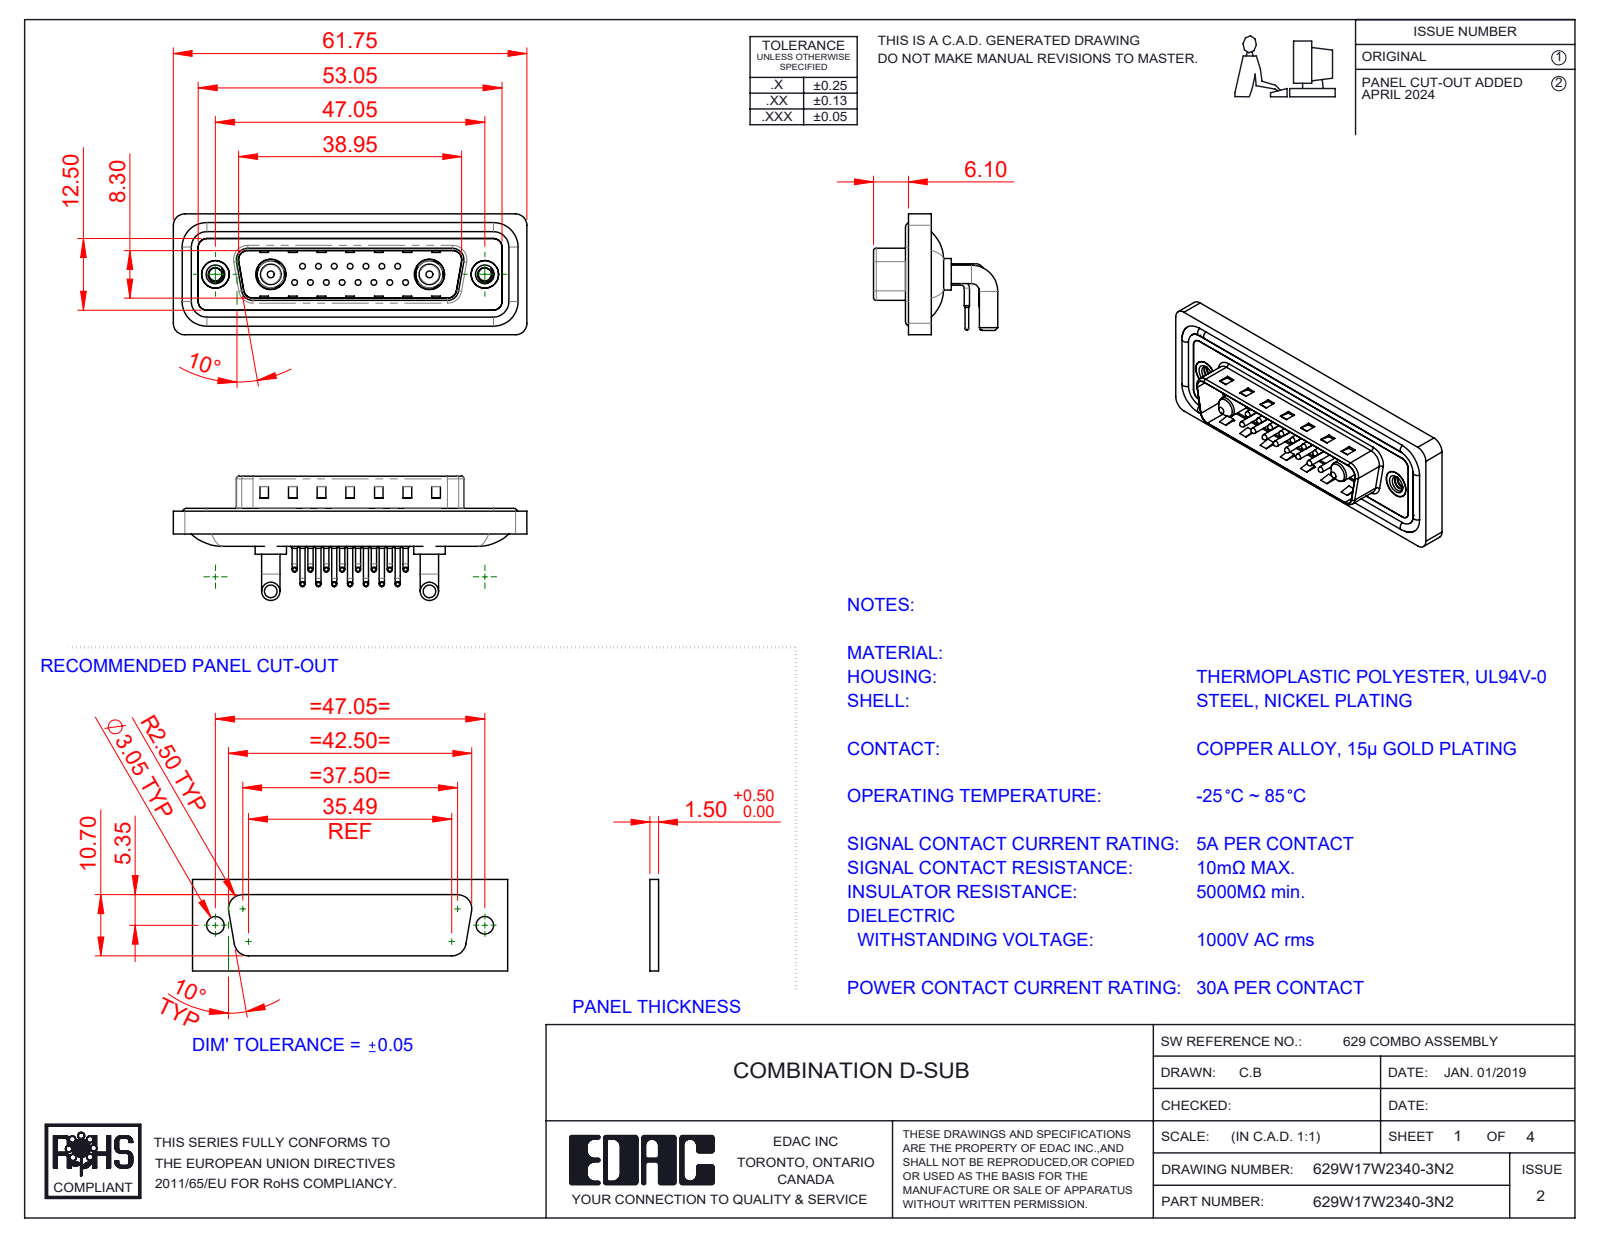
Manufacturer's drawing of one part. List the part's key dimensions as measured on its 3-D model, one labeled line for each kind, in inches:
Part name (STEP PRODUCT): 629Combo Contact Row 1; 629Combo Shell Rear_25 Contacts; 629Combo Contact Row 2; 629Combo Waterproof Housing_25 Contacts (+5 more)
STEP written by: SolidWorks 2023 (CONFIG_CONTROL_DESIGN)
Units: inches
Bodies: 26 solids, 2219 faces (1189 planar, 770 cylindrical, 260 other)
Overall size (bounding box): 2.431 × 0.854 × 0.831
Volume: 0.462 in³ · Surface area: 19.59 in²
Round holes (diameter × count): ⌀0.03 ×15, ⌀0.063 ×15, ⌀0.079 ×15, ⌀0.089 ×2, ⌀0.157 ×2, ⌀0.189 ×2, ⌀0.191 ×2, ⌀0.197 ×2, ⌀0.209 ×2
Round bosses / shafts (diameter × count): ⌀0.035 ×30, ⌀0.059 ×15, ⌀0.039 ×15, ⌀0.026 ×15, ⌀0.126 ×4, ⌀0.063 ×4, ⌀0.217 ×2, ⌀0.205 ×2
Partial cylindrical surfaces — rounded edges, fillets, slot ends (radius × count): R0.059 ×18, R0.079 ×18, R0.04 ×15, R0.02 ×8, R0.063 ×8, R0.01 ×4, R0.024 ×4, R0.026 ×4
Main face-to-face distances: 0.016, 0.114, 0.031, 0.161, 0.043, 0.083, 0.063, 0.177, 0.059, 0.098
Hole centre spacings: 0.124, 0.109, 0.218, 0.327, 0.198, 0.295, 0.436, 0.198
